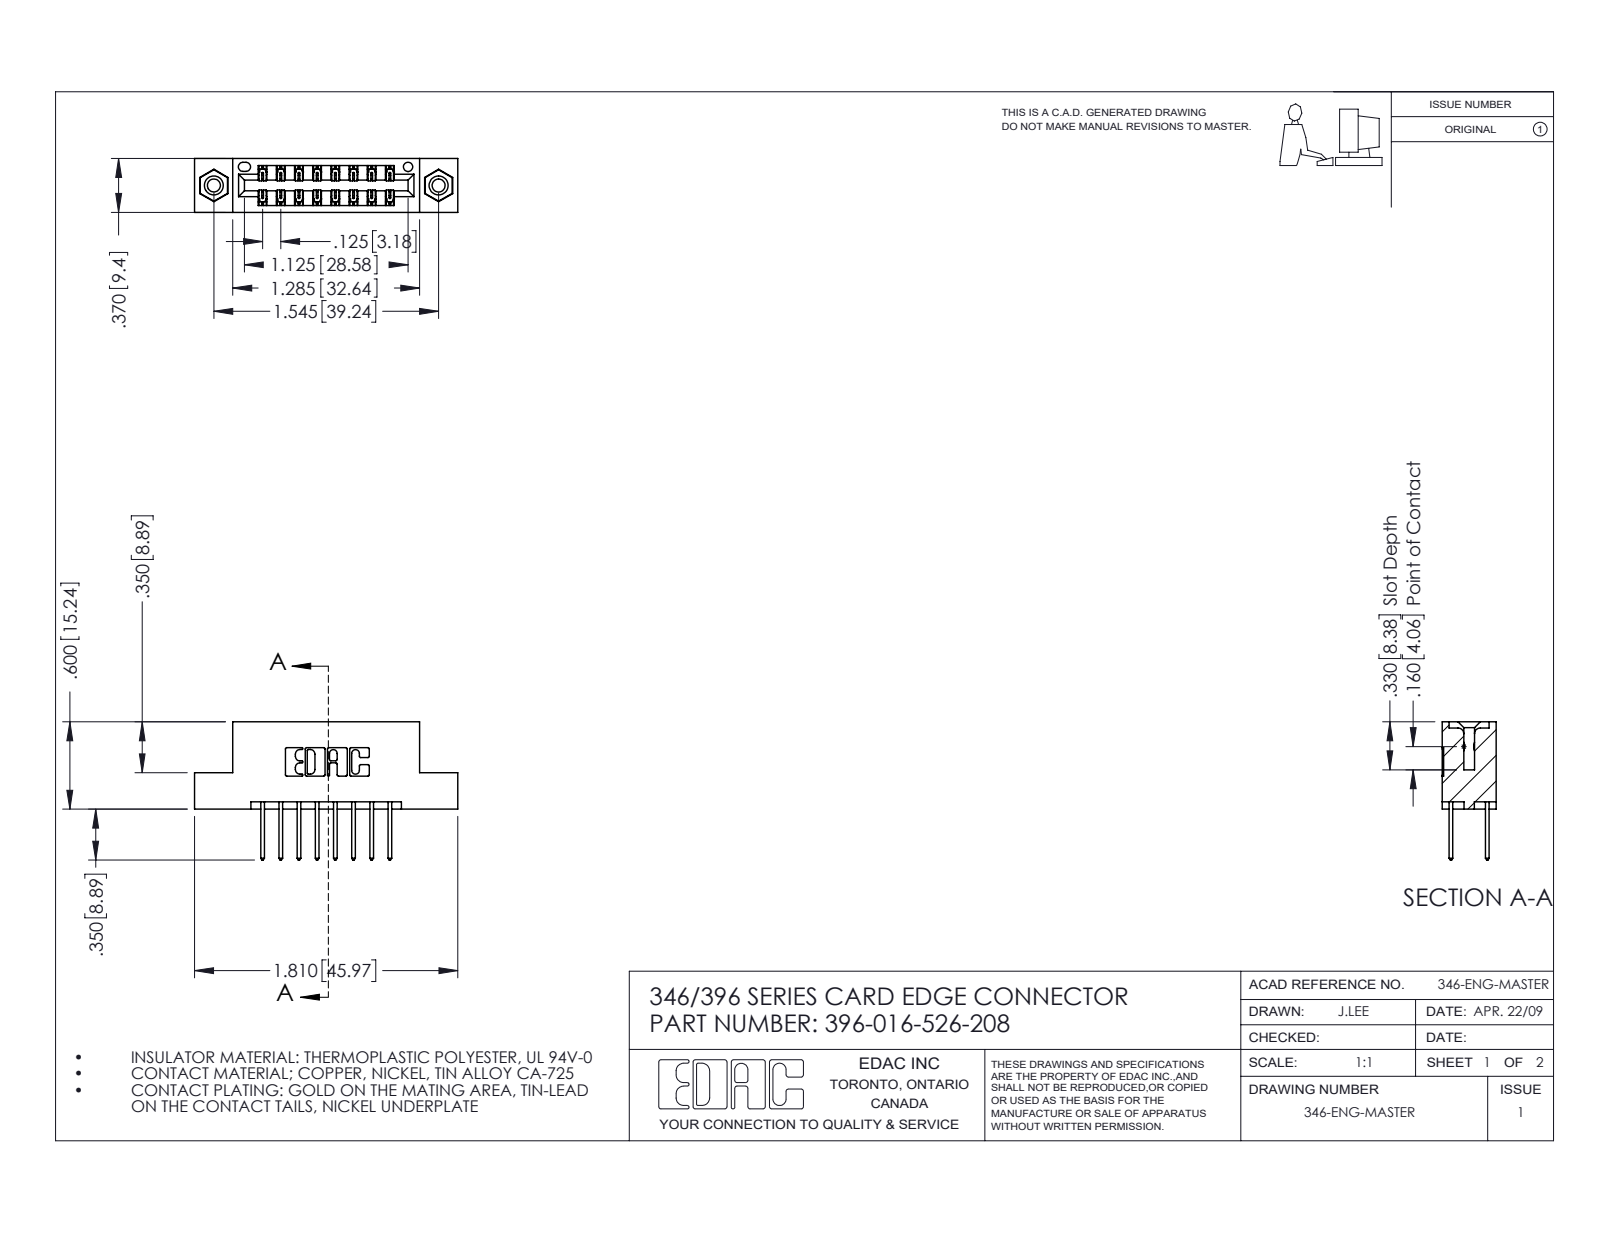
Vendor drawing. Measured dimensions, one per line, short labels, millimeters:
name: 346 Part_Flush Mounting Lugs - 0.156 Dia-TI; 345-292-001_345-293-126; 396-016-526-208; 345-250-001_345-250-003-102
written by: SolidWorks 2016 (CONFIG_CONTROL_DESIGN)
unit: mm
bodies: 19 solids, 1014 faces (668 planar, 330 cylindrical, 16 other)
size: 46 × 24.1 × 9.4
volume: 4 240 mm³; area: 5 430 mm²
holes: 2× ⌀2.3, 2× ⌀3.2, 2× ⌀4, 1× ⌀1.6
bosses: 2× ⌀3.9
rounds: 24× R0.2, 22× R0.3, 16× R0.3, 6× R0.2, 6× R0.8, 3× R0.7, 2× R0.4, 2× R0.6
face distances: 6.4, 1.2, 8.2, 9.4, 1.8, 7.6, 0.6, 7, 12.7, 3.8
hole spacings: 6.2, 34.1, 39.2
